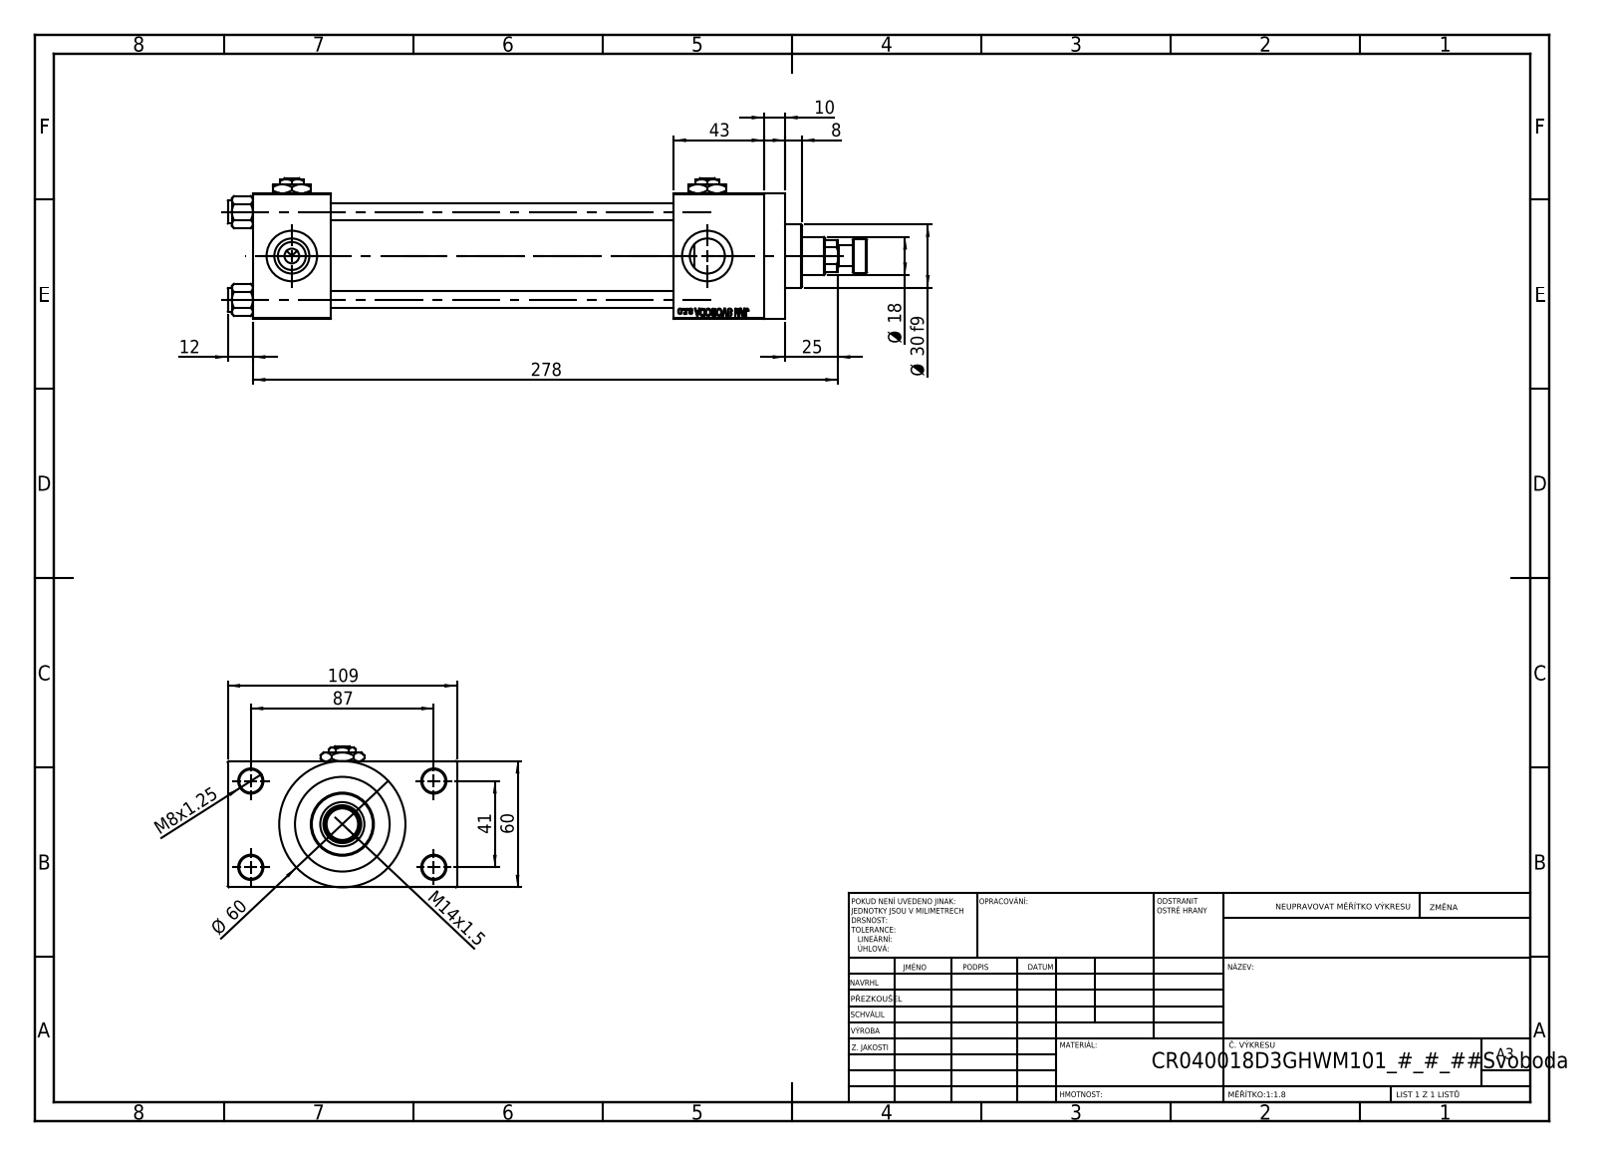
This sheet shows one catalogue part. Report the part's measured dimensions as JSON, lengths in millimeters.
{"part_name": "V215CR_D_TYCINKA; V215CR_VCP_D; V215CR_ROD_END_W; V215_VC_A (+3 more)", "step_written_by": "SolidWorks 2019 (CONFIG_CONTROL_DESIGN)", "units": "millimeters", "bodies": {"solids": 14, "faces": 1218, "planar": 549, "cylindrical": 103, "other": 566}, "overall_size": [304, 109, 67], "volume_mm3": 602677, "surface_area_mm2": 171030, "round_holes": [[8, 4], [11, 4], [16.66, 4], [24, 4], [7, 3], [8.5, 1], [18, 1], [21, 1], [31, 1], [40, 1], [45, 1]], "round_bosses_or_shafts": [[11, 4], [60, 1], [46, 1], [30, 1], [16, 1], [10, 1]], "partial_cylinders_radius": [[8.5, 1]], "face_to_face_distances": [60, 24.5, 163, 84.5, 37, 200, 43, 243, 206, 10], "hole_center_spacings": [22.65, 29.49, 41.7, 47.15, 48.09, 64.35, 76.49, 41]}
